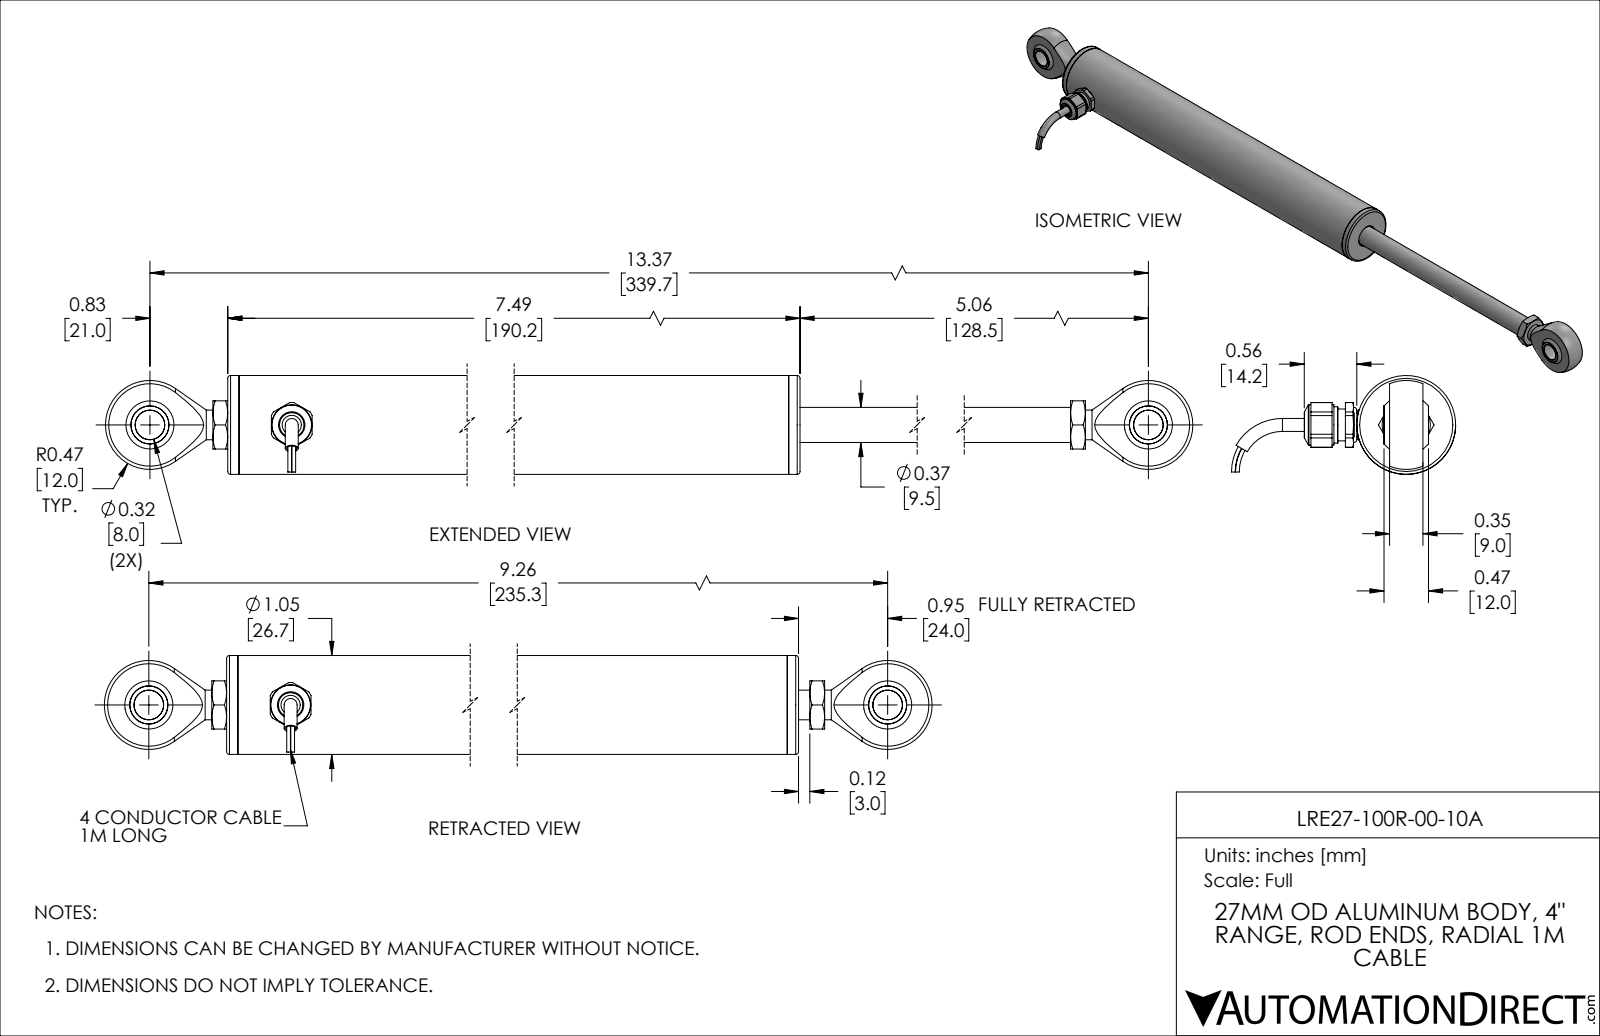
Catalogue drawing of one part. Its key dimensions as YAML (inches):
part_name: "LRE27-100R-00-10A"
step_written_by: "SolidWorks 2019 (AUTOMOTIVE_DESIGN)"
units: inches
bodies: {solids: 25, faces: 285, planar: 108, cylindrical: 83, other: 94}
overall_size: [10.088, 2.382, 1.05]
volume: 4.539
surface_area: 93.39
round_holes:
  - {diameter: 0.268, count: 2}
  - {diameter: 0.315, count: 2}
  - {diameter: 0.106, count: 1}
  - {diameter: 0.138, count: 1}
  - {diameter: 0.156, count: 1}
  - {diameter: 0.187, count: 1}
  - {diameter: 0.201, count: 1}
  - {diameter: 0.205, count: 1}
  - {diameter: 0.25, count: 1}
  - {diameter: 0.274, count: 1}
  - {diameter: 0.313, count: 1}
  - {diameter: 0.36, count: 1}
round_bosses_or_shafts:
  - {diameter: 0.039, count: 4}
  - {diameter: 0.315, count: 2}
  - {diameter: 1.05, count: 1}
  - {diameter: 0.85, count: 1}
  - {diameter: 0.848, count: 1}
  - {diameter: 0.687, count: 1}
  - {diameter: 0.685, count: 1}
  - {diameter: 0.625, count: 1}
partial_cylinders:
  - {radius: 0.01, count: 2}
  - {radius: 0.067, count: 2}
  - {radius: 0.25, count: 2}
  - {radius: 0.197, count: 1}
  - {radius: 0.224, count: 1}
  - {radius: 0.238, count: 1}
face_to_face_distances: [0.12, 7.37, 0.354, 7.49, 0.862, 6.628, 5.161, 1.65, 0.788, 5.84]
hole_center_spacings: [1.507, 7.637, 9.144]
